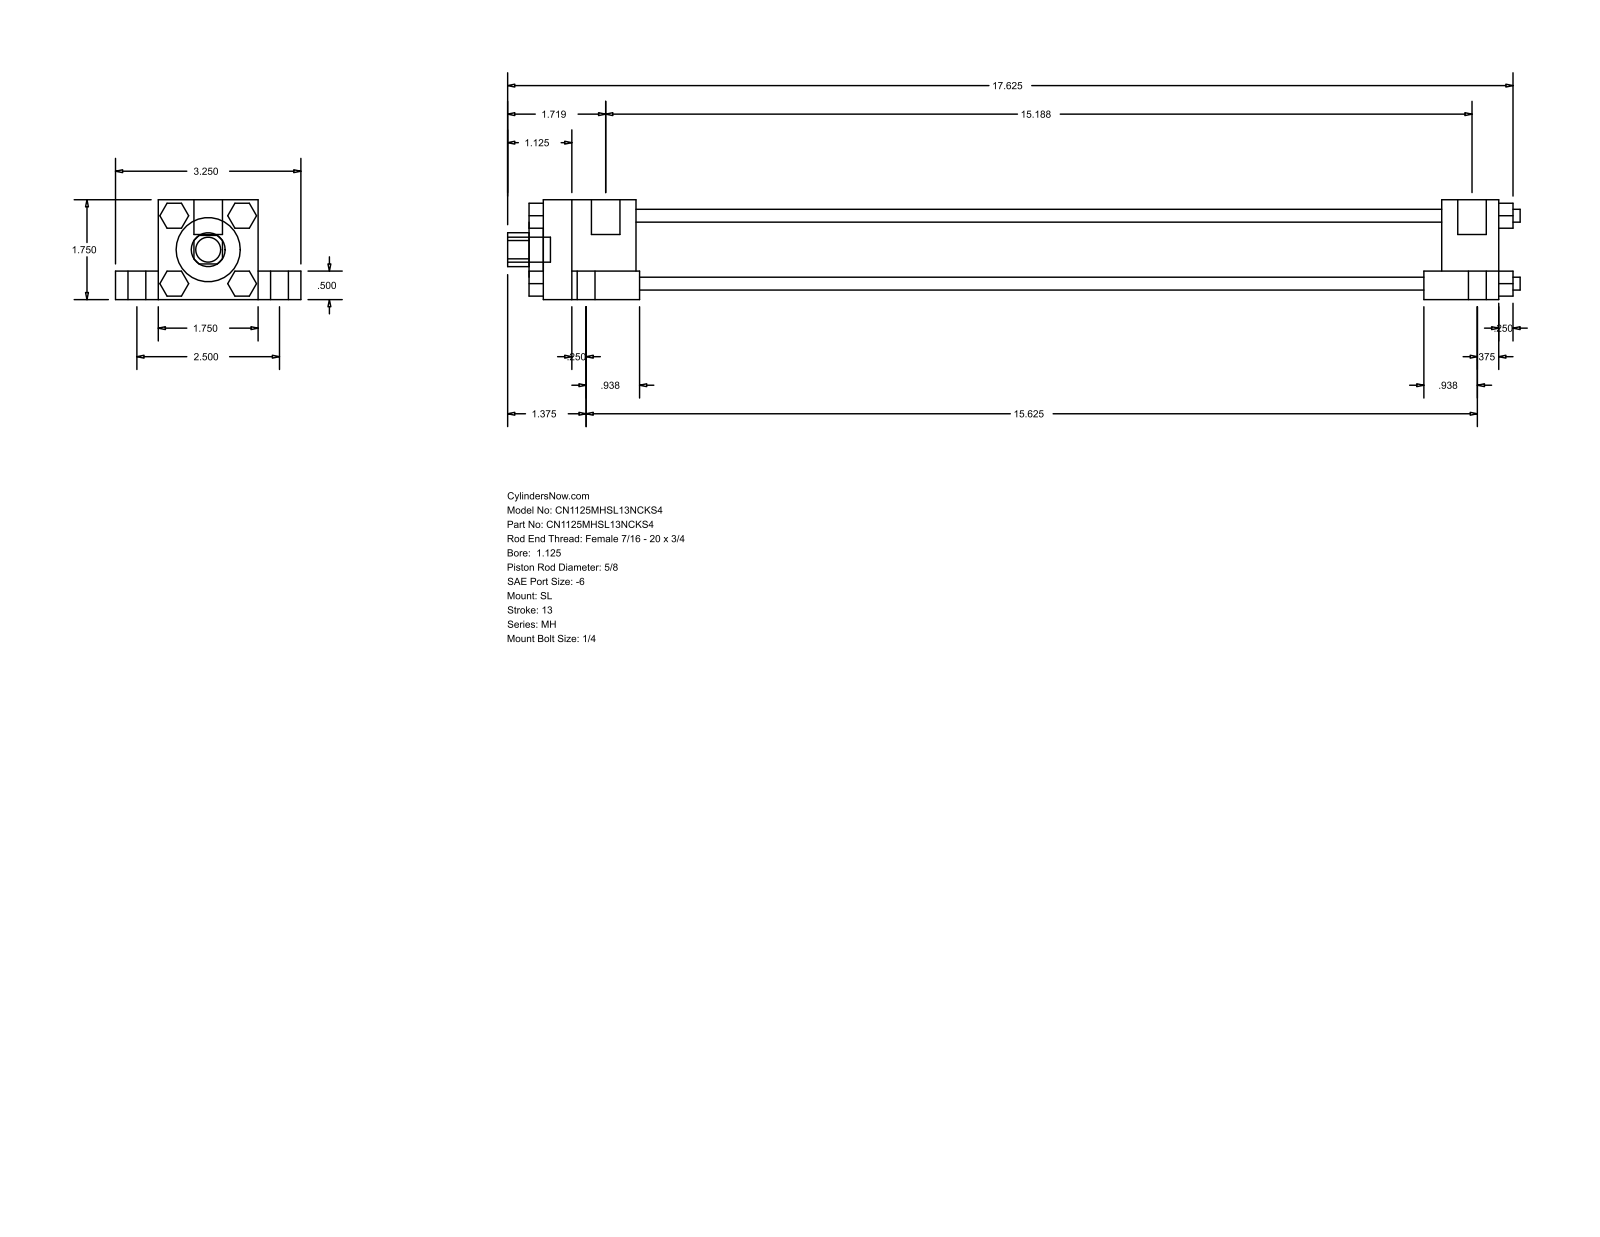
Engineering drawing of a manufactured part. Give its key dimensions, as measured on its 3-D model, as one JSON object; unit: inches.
{"part_name": "MH_SL__0112_0.625", "step_written_by": "GSSL Pune (CONFIG_CONTROL_DESIGN)", "units": "inches", "bodies": {"solids": 0, "faces": 150, "planar": 114, "cylindrical": 36, "other": 0}, "overall_size": [17.75, 3.25, 1.75], "round_holes": [[0.625, 1], [1.125, 1], [1.375, 1]], "round_bosses_or_shafts": [[0.563, 4], [0.313, 4], [0.225, 4], [0.219, 4], [0.5, 2], [0.437, 1]], "partial_cylinders_radius": [[0.297, 1]], "face_to_face_distances": [1.75, 0.75, 0.5, 1.25, 2.5, 0.437, 14.125, 15.125, 1, 1.625]}
